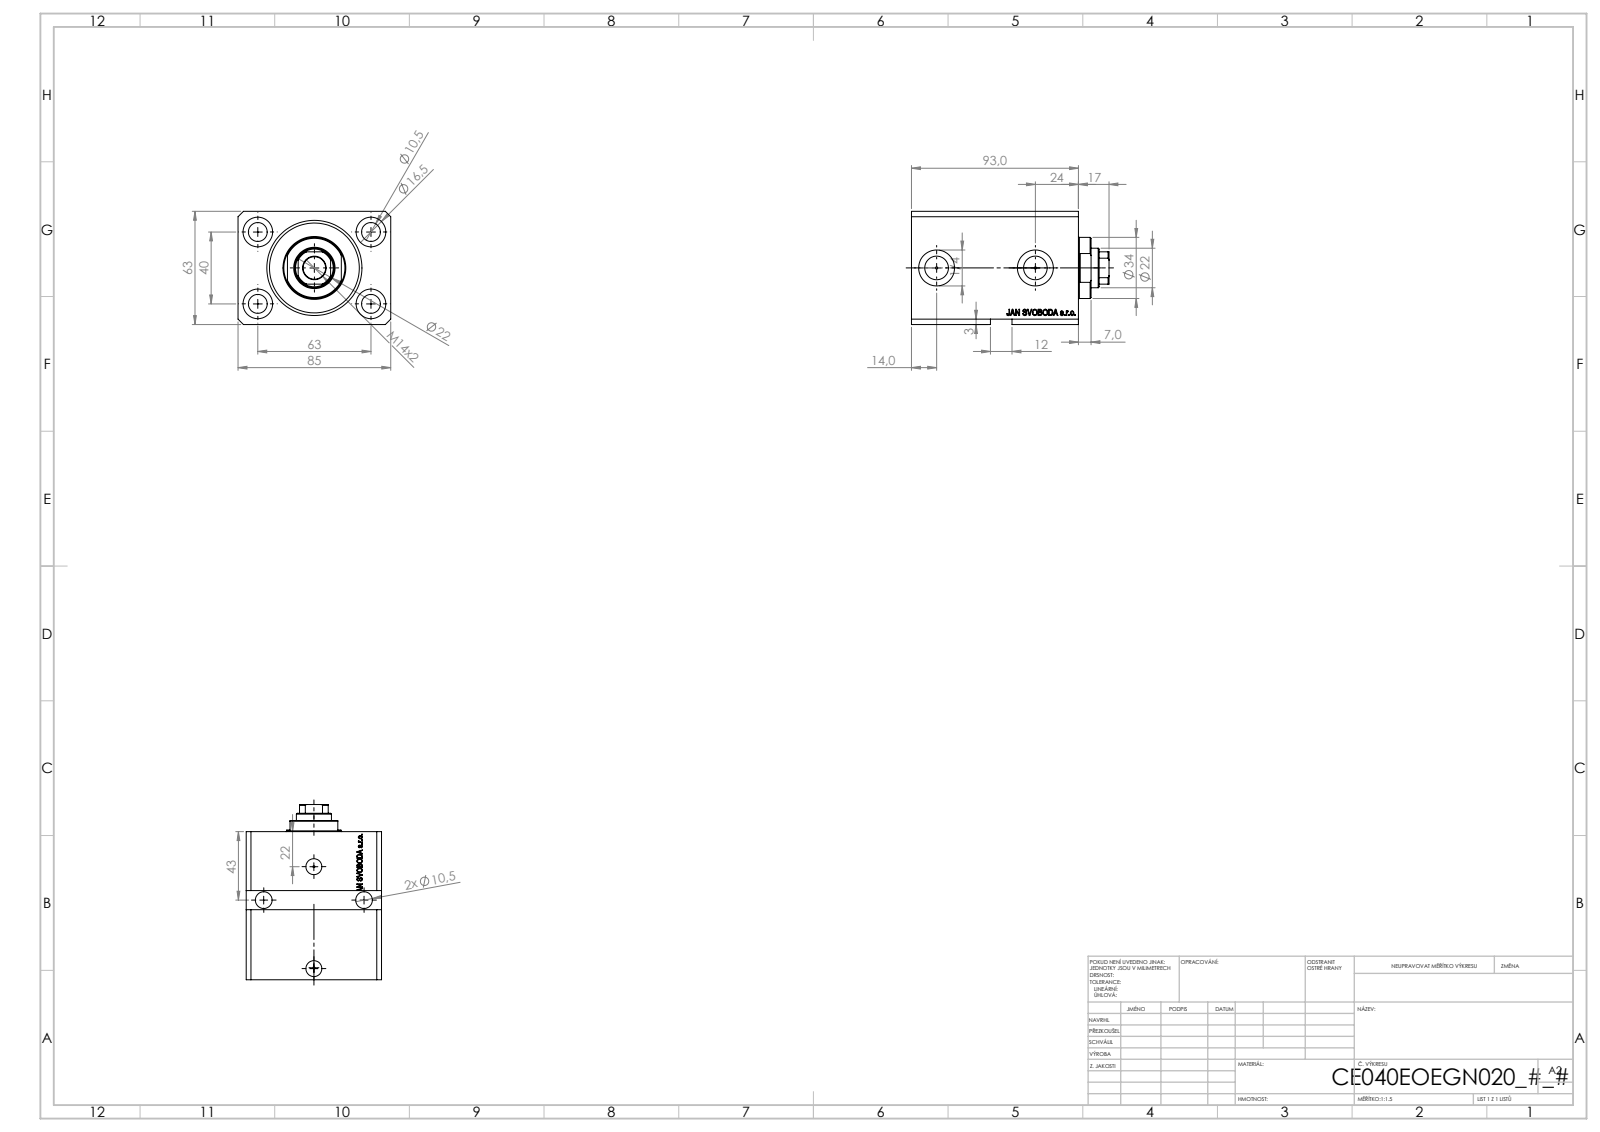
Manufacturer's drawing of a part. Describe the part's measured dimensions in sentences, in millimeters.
The part is named "V250CE_VC_E; V250CE_C_VCP; V250CE_E_Body". Its 3-D file was written by "SolidWorks 2019 (CONFIG_CONTROL_DESIGN)". It is 3 solids with 917 faces: 459 planar, 84 cylindrical and 374 other. Overall it measures 110 by 85 by 63 millimeters. Its volume is 427 173 cubic millimeters and its surface area 87 247 square millimeters. Round holes: 6 of diameter 10.5, 4 of diameter 1.25, 4 of diameter 16.5, 2 of diameter 10, 2 of diameter 13.16, 2 of diameter 20, 1 of diameter 12.5, 1 of diameter 22, 1 of diameter 40, 1 of diameter 53. Round bosses or shafts: 1 of diameter 34. Partial cylindrical surfaces (rounded edges, fillets, slot ends): 1 of radius 10.5. The main face-to-face distances are 63, 85, 93, 17, 76, 11.4, 64.6, 81.6, 56, 44.6. The hole center spacings are 37.31, 63, 37.86, 40, 52.88, 53.3, 74.63, 0.53.
